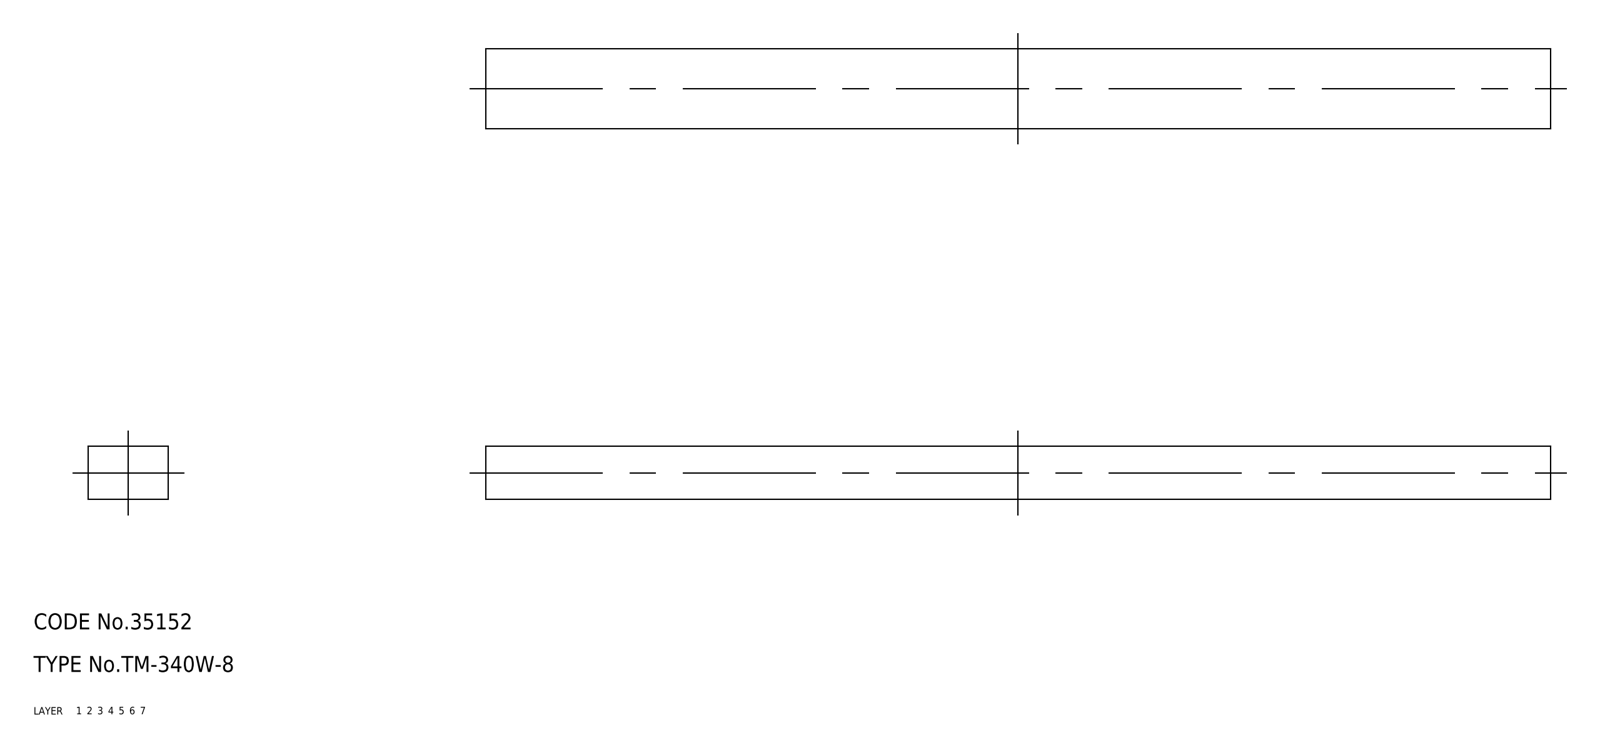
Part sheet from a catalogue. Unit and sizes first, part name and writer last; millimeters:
Units: millimetres
Overall size (bounding box): 200 × 15 × 10
Main face-to-face distances: 10, 15, 200
Volume: 30 000 mm³ · Surface area: 10 300 mm²
Bodies: 1 solid, 6 faces (6 planar, 0 cylindrical, 0 other)
Part name (STEP PRODUCT): rubber foam; TM_340W_8
STEP written by: SolidWorks 2015 (AUTOMOTIVE_DESIGN)
